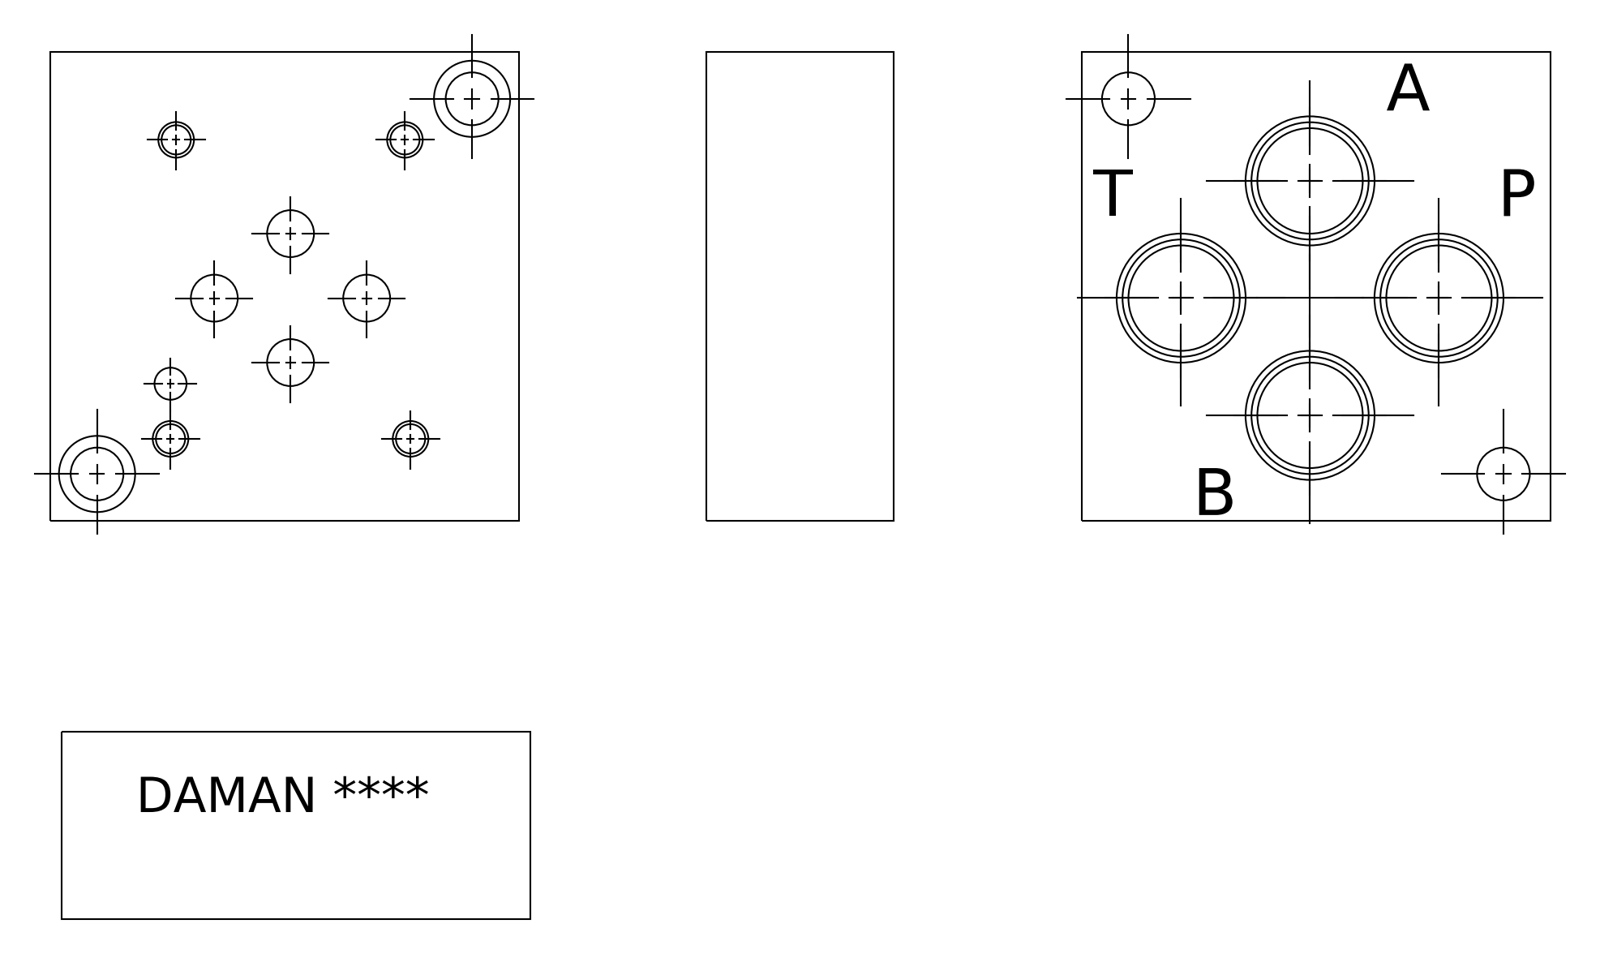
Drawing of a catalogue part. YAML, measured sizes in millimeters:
part_name: "Part_AD03SPB6P.B00094R11_3D"
step_written_by: "Autodesk Inventor 2019 (AUTOMOTIVE_DESIGN)"
units: millimeters
bodies: {solids: 1, faces: 448, planar: 276, cylindrical: 25, other: 147}
overall_size: [63.5, 63.5, 25.4]
volume: 85002
surface_area: 20515
round_holes:
  - {diameter: 7.14, count: 6}
  - {diameter: 3.78, count: 4}
  - {diameter: 4.83, count: 4}
  - {diameter: 14.3, count: 4}
  - {diameter: 17.3, count: 4}
  - {diameter: 10.31, count: 2}
  - {diameter: 3.96, count: 1}
face_to_face_distances: [63.5, 25.4, 11.73, 13.67, 12.7, 1, 62.5, 0.97, 10.73, 11.7]
hole_center_spacings: [7.13, 7.14, 13.52, 13.54, 19.12, 21.5, 22.05, 33.55]
